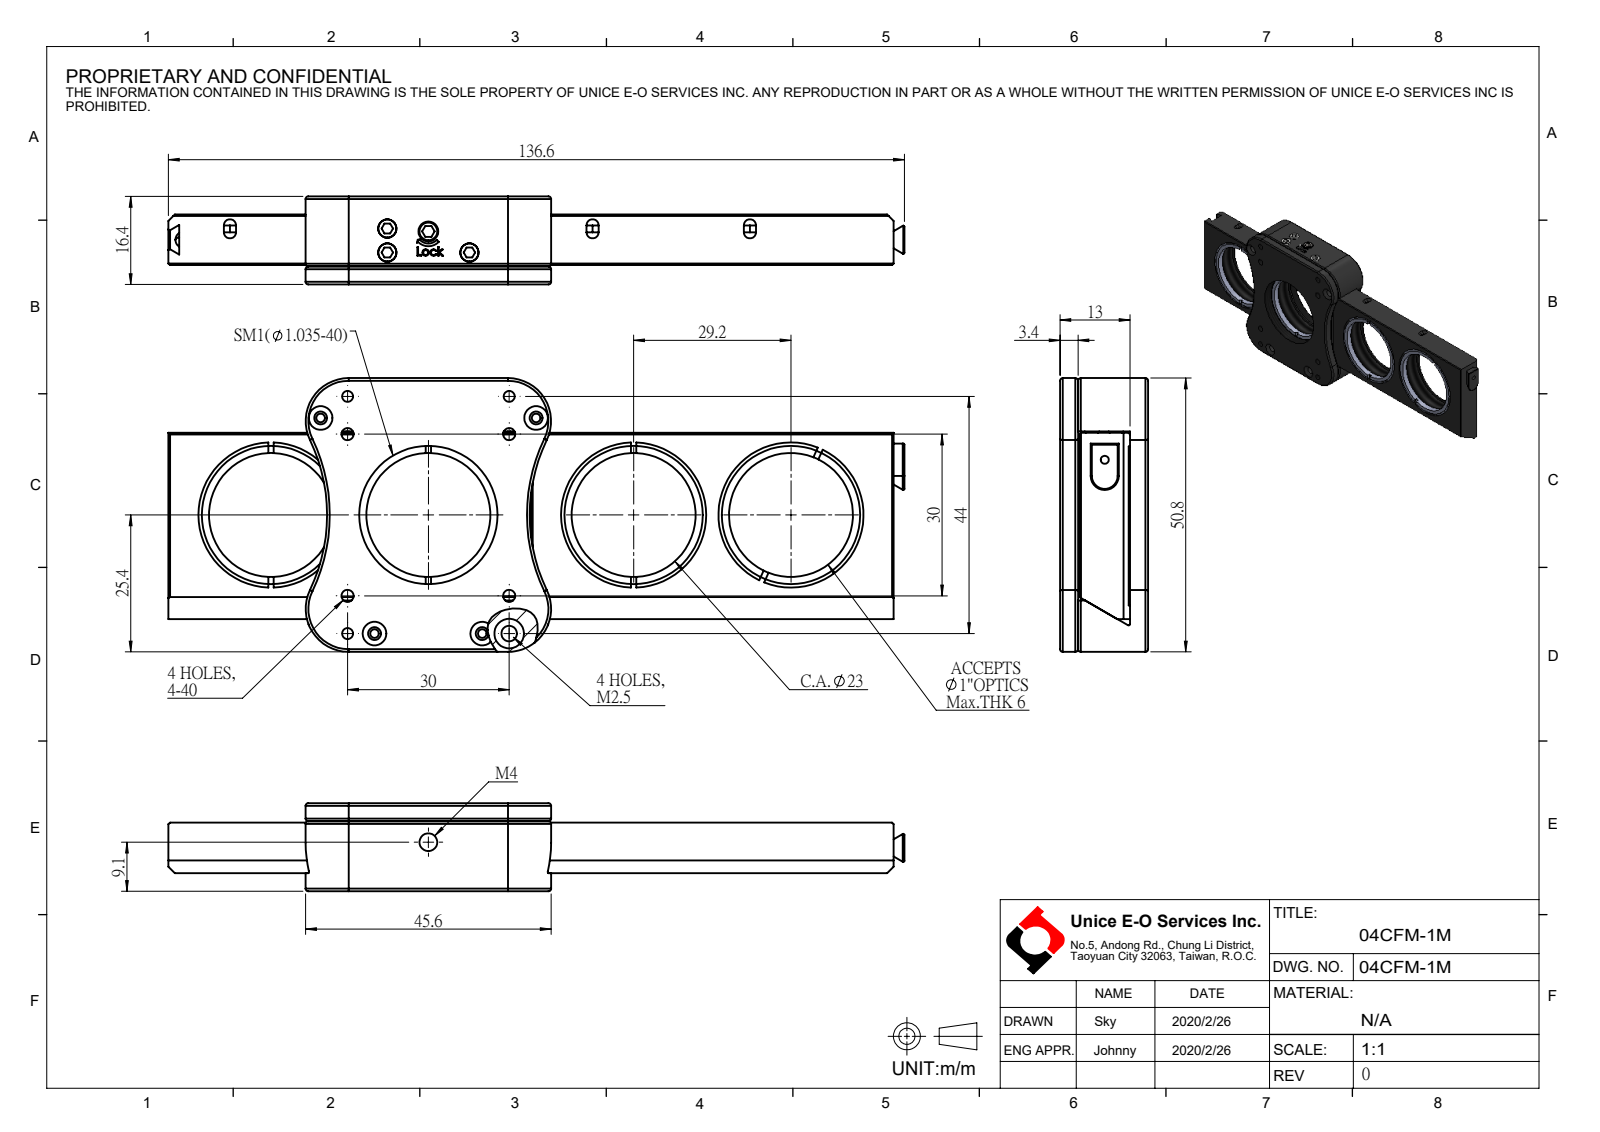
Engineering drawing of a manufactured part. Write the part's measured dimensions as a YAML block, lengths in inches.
part_name: "04CFM-1M"
step_written_by: "SolidWorks 2016 (AUTOMOTIVE_DESIGN)"
units: inches
bodies: {solids: 0, faces: 354, planar: 167, cylindrical: 123, other: 64}
overall_size: [5.379, 2, 0.644]
round_holes:
  - {diameter: 0.081, count: 4}
  - {diameter: 0.089, count: 4}
  - {diameter: 0.094, count: 4}
  - {diameter: 0.114, count: 4}
  - {diameter: 0.906, count: 4}
  - {diameter: 0.945, count: 4}
  - {diameter: 1.01, count: 4}
  - {diameter: 0.13, count: 1}
  - {diameter: 0.181, count: 1}
partial_cylinders:
  - {radius: 0.02, count: 8}
  - {radius: 0.008, count: 5}
  - {radius: 0.315, count: 4}
  - {radius: 1.26, count: 2}
  - {radius: 0.01, count: 1}
  - {radius: 0.108, count: 1}
  - {radius: 0.118, count: 1}
face_to_face_distances: [0.37, 0.132, 0.142, 0.502, 0.512, 0.36, 0.38, 0.644, 0.079, 0.26]
hole_center_spacings: [1.181, 0.276, 0.835, 1.048, 1.213, 1.457, 1.875, 1.15]
